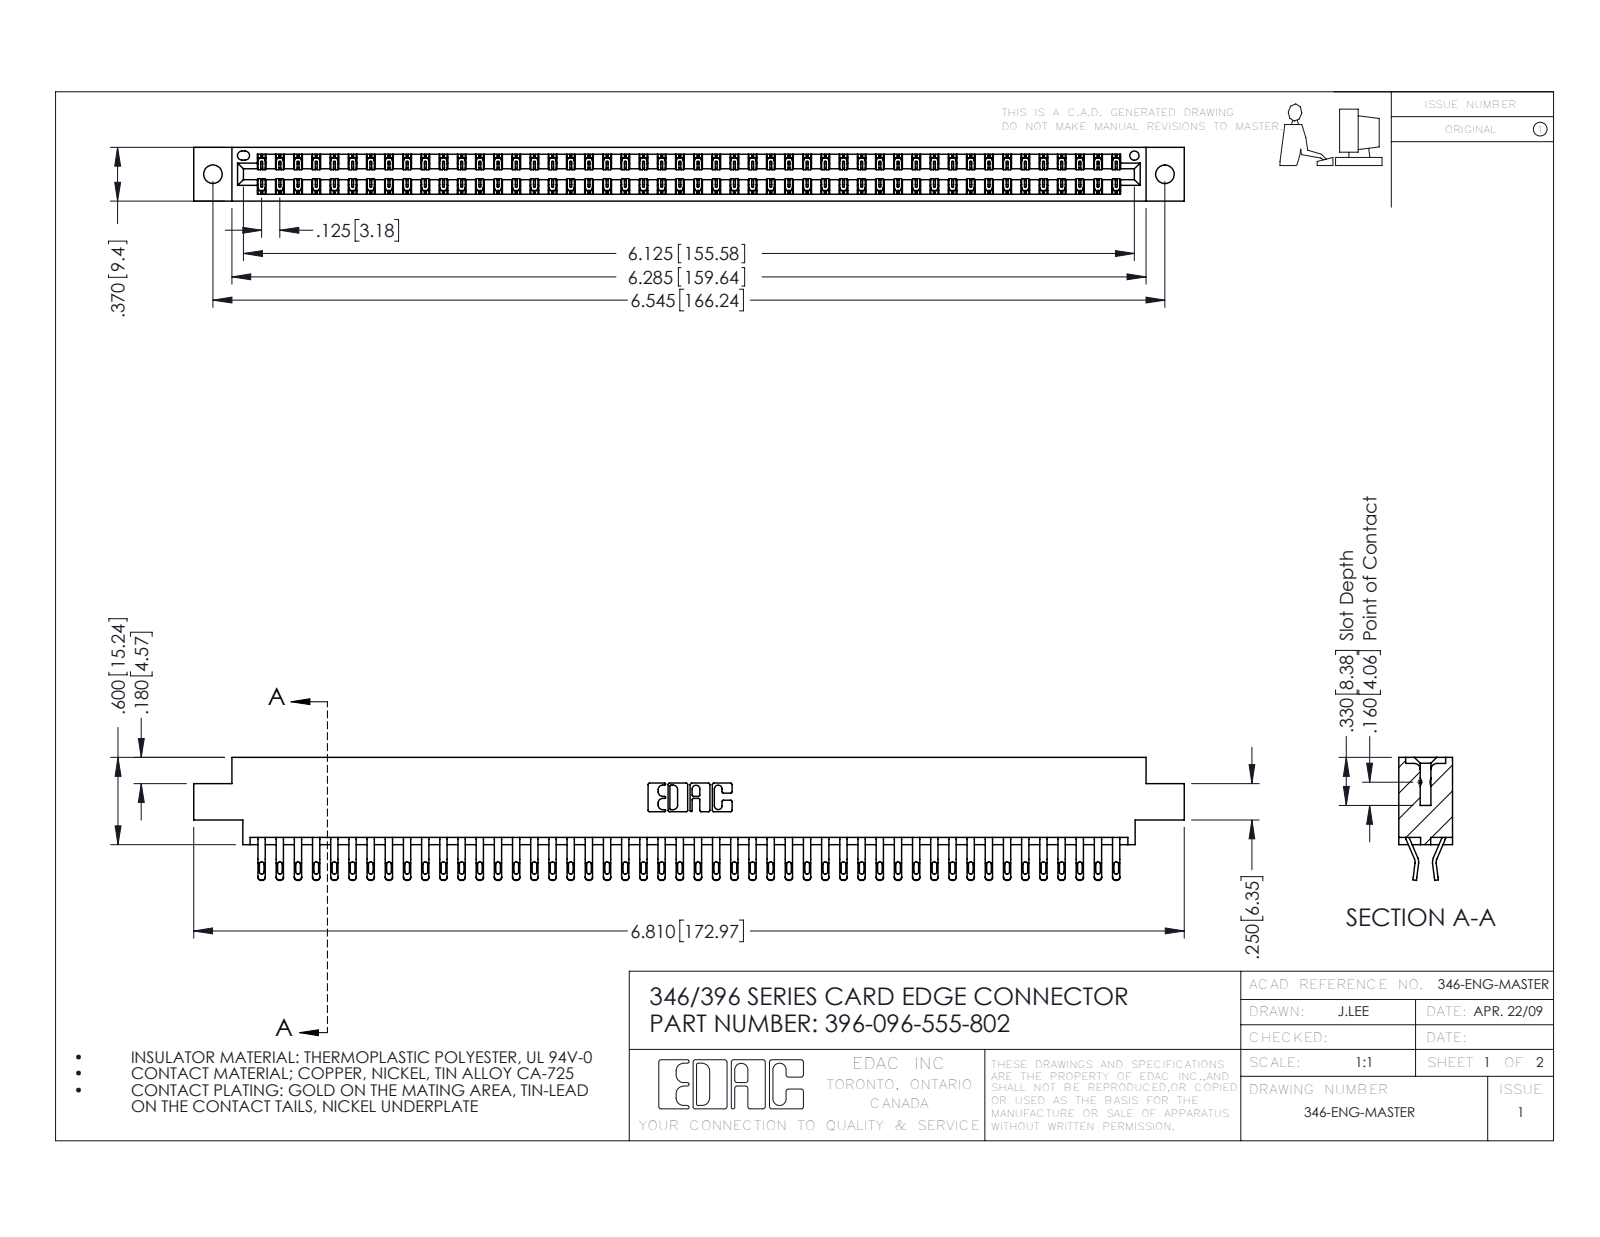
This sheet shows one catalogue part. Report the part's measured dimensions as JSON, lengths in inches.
{"part_name": "346 Part_0.170 Offset - 0.128 Dia; 345-292-001_555 Tail; 396-096-555-802", "step_written_by": "SolidWorks 2016 (CONFIG_CONTROL_DESIGN)", "units": "inches", "bodies": {"solids": 97, "faces": 5694, "planar": 3248, "cylindrical": 2446, "other": 0}, "overall_size": [6.81, 0.845, 0.37], "volume_in3": 1.037, "surface_area_in2": 37.77, "round_holes": [[0.128, 2], [0.064, 1]], "partial_cylinders_radius": [[0.016, 192], [0.02, 192], [0.006, 144], [0.01, 22], [0.007, 6], [0.031, 6], [0.026, 3], [0.01, 2]], "face_to_face_distances": [0.048, 0.322, 0.37, 0.25, 0.025, 0.072, 0.298, 0.275, 0.148, 0.222], "hole_center_spacings": [0.246, 6.336, 6.545]}
